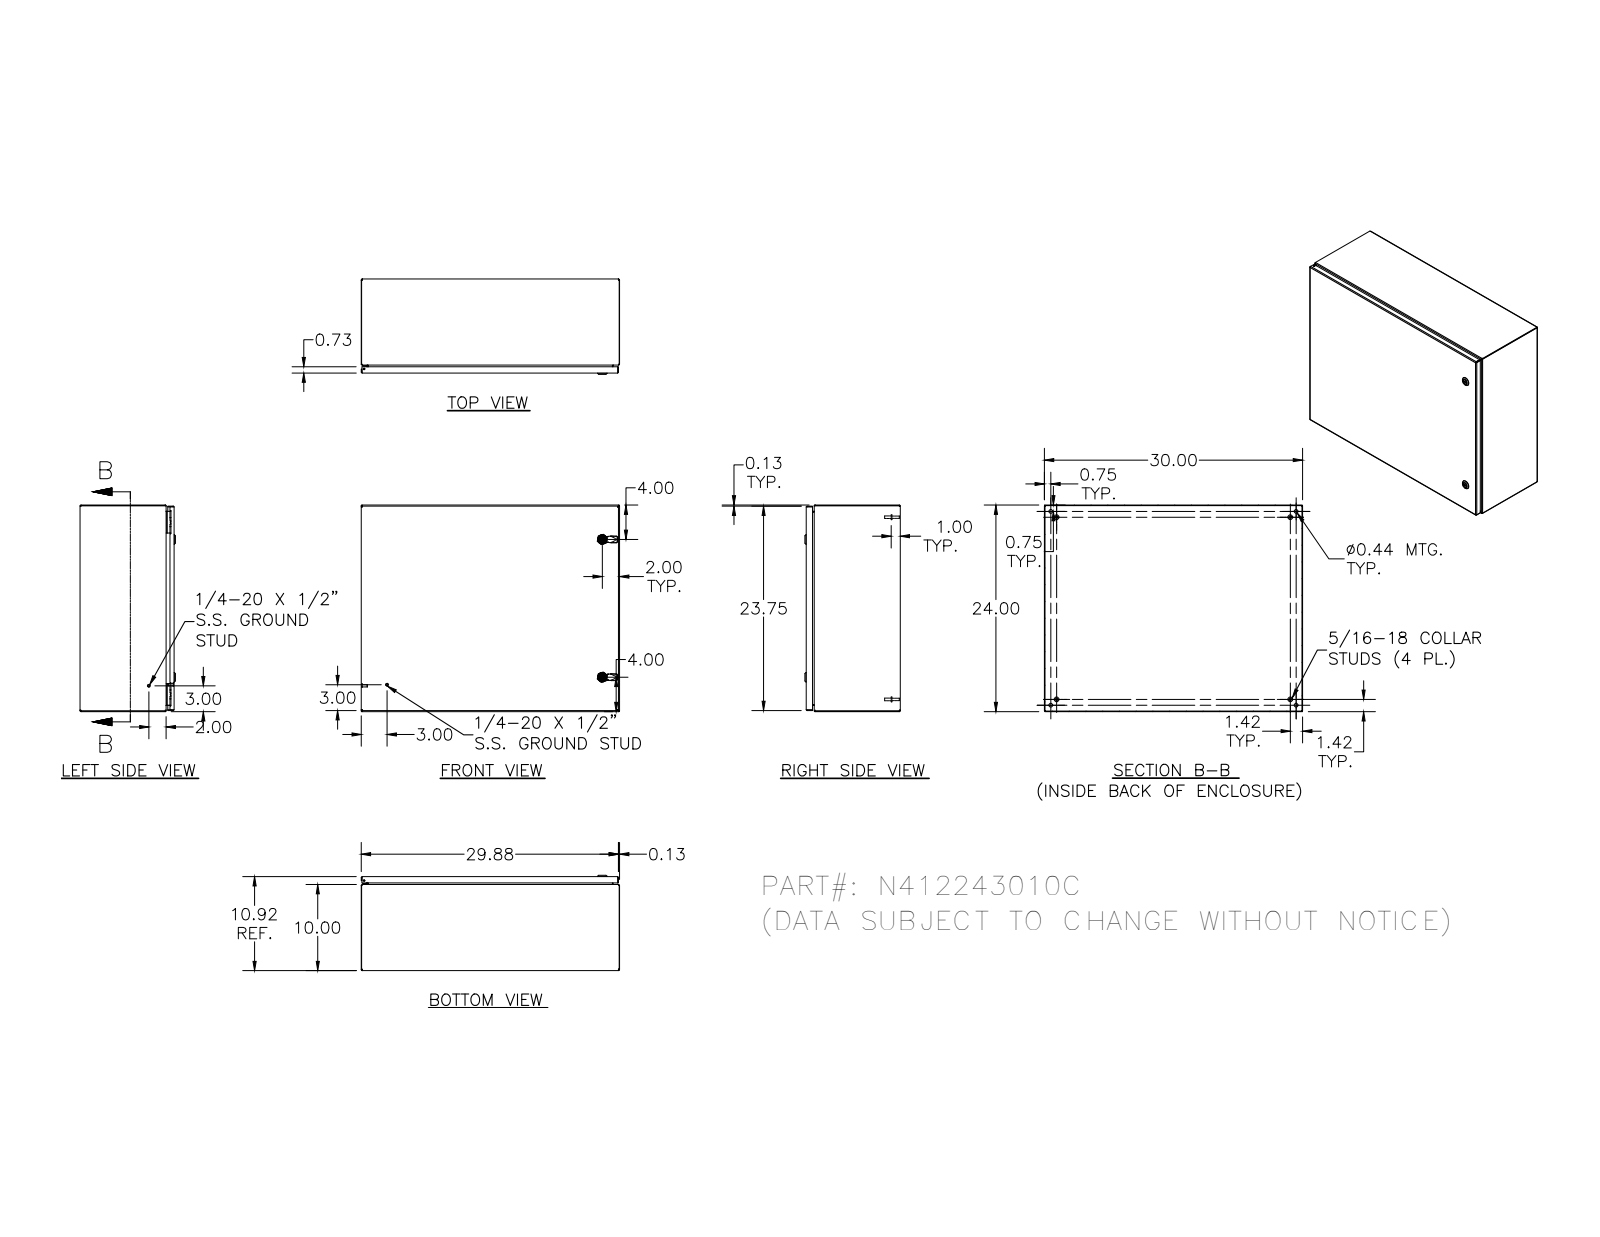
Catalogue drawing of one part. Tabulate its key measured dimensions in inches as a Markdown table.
| quantity | value |
| --- | --- |
| part name | N412243010C; N4122430CLID; 35124; 1000-u155_asm (+8 more) |
| STEP written by | Autodesk Inventor 2011 (AUTOMOTIVE_DESIGN) |
| units | inches |
| bodies | 38 solids, 1816 faces (706 planar, 678 cylindrical, 432 other) |
| overall size | 30 × 24 × 11.075 |
| volume | 202.3 in³ |
| surface area | 5 506 in² |
| round holes (diameter × count) | 0.188 × 5, 0.093 × 4, 0.152 × 4, 0.167 × 4, 0.172 × 4, 0.437 × 4, 0.156 × 2, 0.197 × 2, 0.315 × 2, 0.394 × 2, 0.402 × 2, 0.634 × 2 |
| round bosses / shafts (diameter × count) | 0.25 × 10, 0.563 × 4, 0.36 × 4, 0.32 × 4, 0.3 × 4, 0.275 × 4, 0.256 × 4, 0.164 × 4 |
| partial cylindrical surfaces (radius × count) | 0.012 × 54, 0.031 × 30, 0.05 × 26, 0.02 × 23, 0.105 × 20, 0.016 × 18, 0.125 × 16, 0.032 × 8 |
| main face-to-face distances | 0.074, 10.843, 10.769, 10.917, 0.074, 23.926, 24, 23.852, 23.926, 29.926 |
| hole center spacings | 20, 0.66, 0.656, 1.307, 1.965, 19.34, 19.996, 20.656 |
